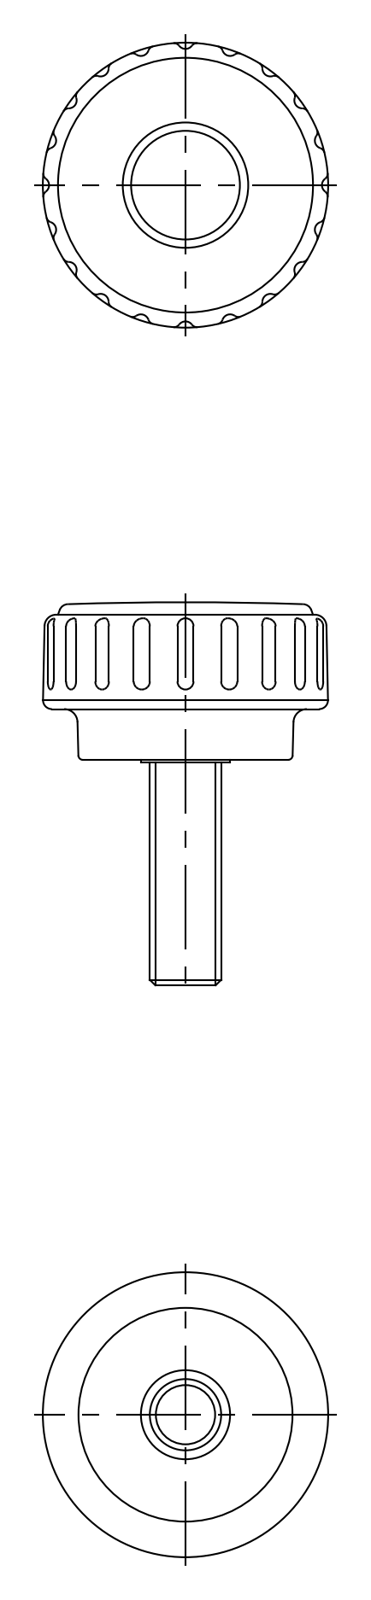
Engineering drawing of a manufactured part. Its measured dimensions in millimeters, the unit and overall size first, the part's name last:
Units: millimetres
Overall size (bounding box): 42.94 × 32.03 × 31.96
Volume: 12 763 mm³ · Surface area: 4 358 mm²
Bodies: 2 solids, 69 faces (0 planar, 0 cylindrical, 69 other)
Part name (STEP PRODUCT): screw; knob; KDMS_32_M8_25_WH_24173_36
STEP written by: CADfix (AUTOMOTIVE_DESIGN)
